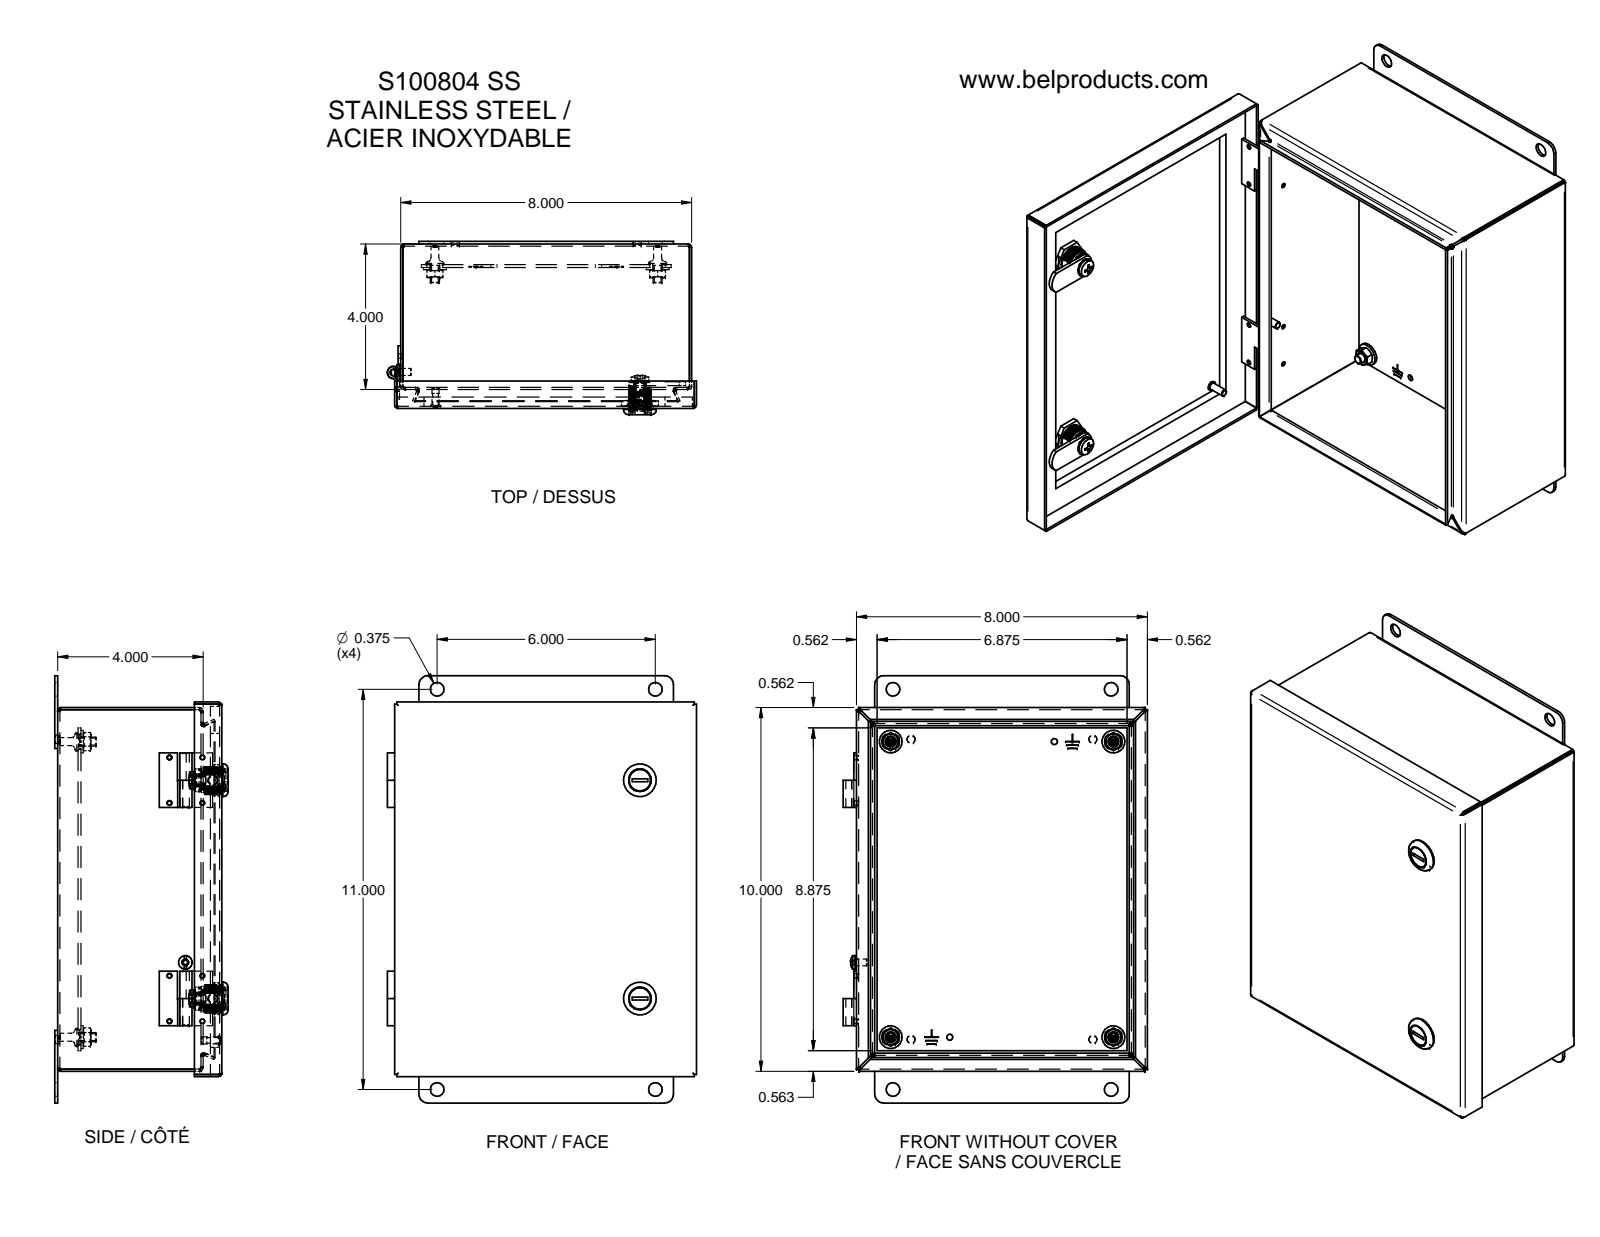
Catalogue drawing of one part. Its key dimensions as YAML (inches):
part_name: "LOCK AVEC TOURNEVIS TYPE 4-12 SANS CAME-oa8; HOSING-oa0; INSERT POUR TOURNEVIS-oa1; NOIX DE FIXATION-oa2 (+8 more)"
step_written_by: "Unknown (AUTOMOTIVE_DESIGN)"
units: inches
bodies: {solids: 43, faces: 1950, planar: 1134, cylindrical: 334, other: 482}
overall_size: [11.75, 8.502, 4.765]
volume: 35.83
surface_area: 1011
round_holes:
  - {diameter: 0.124, count: 8}
  - {diameter: 0.13, count: 8}
  - {diameter: 0.125, count: 5}
  - {diameter: 0.22, count: 4}
  - {diameter: 0.236, count: 4}
  - {diameter: 0.25, count: 4}
  - {diameter: 0.281, count: 4}
  - {diameter: 0.375, count: 4}
  - {diameter: 0.437, count: 4}
  - {diameter: 0.169, count: 3}
  - {diameter: 0.014, count: 2}
  - {diameter: 0.275, count: 2}
round_bosses_or_shafts:
  - {diameter: 0.125, count: 8}
  - {diameter: 0.119, count: 5}
  - {diameter: 0.625, count: 4}
  - {diameter: 0.225, count: 4}
  - {diameter: 0.219, count: 4}
  - {diameter: 0.031, count: 4}
  - {diameter: 0.9, count: 2}
  - {diameter: 0.89, count: 2}
partial_cylinders:
  - {radius: 0.375, count: 22}
  - {radius: 0.01, count: 16}
  - {radius: 0.032, count: 16}
  - {radius: 0.092, count: 16}
  - {radius: 0.063, count: 8}
  - {radius: 0.25, count: 4}
  - {radius: 0.371, count: 4}
  - {radius: 0.245, count: 2}
face_to_face_distances: [0.06, 4.454, 0.06, 4.514, 0.641, 0.075, 4.394, 4.454, 7.94, 0.581]
hole_center_spacings: [0.907, 6, 0.566, 1.25, 8.207, 5, 5.563, 5.669]
